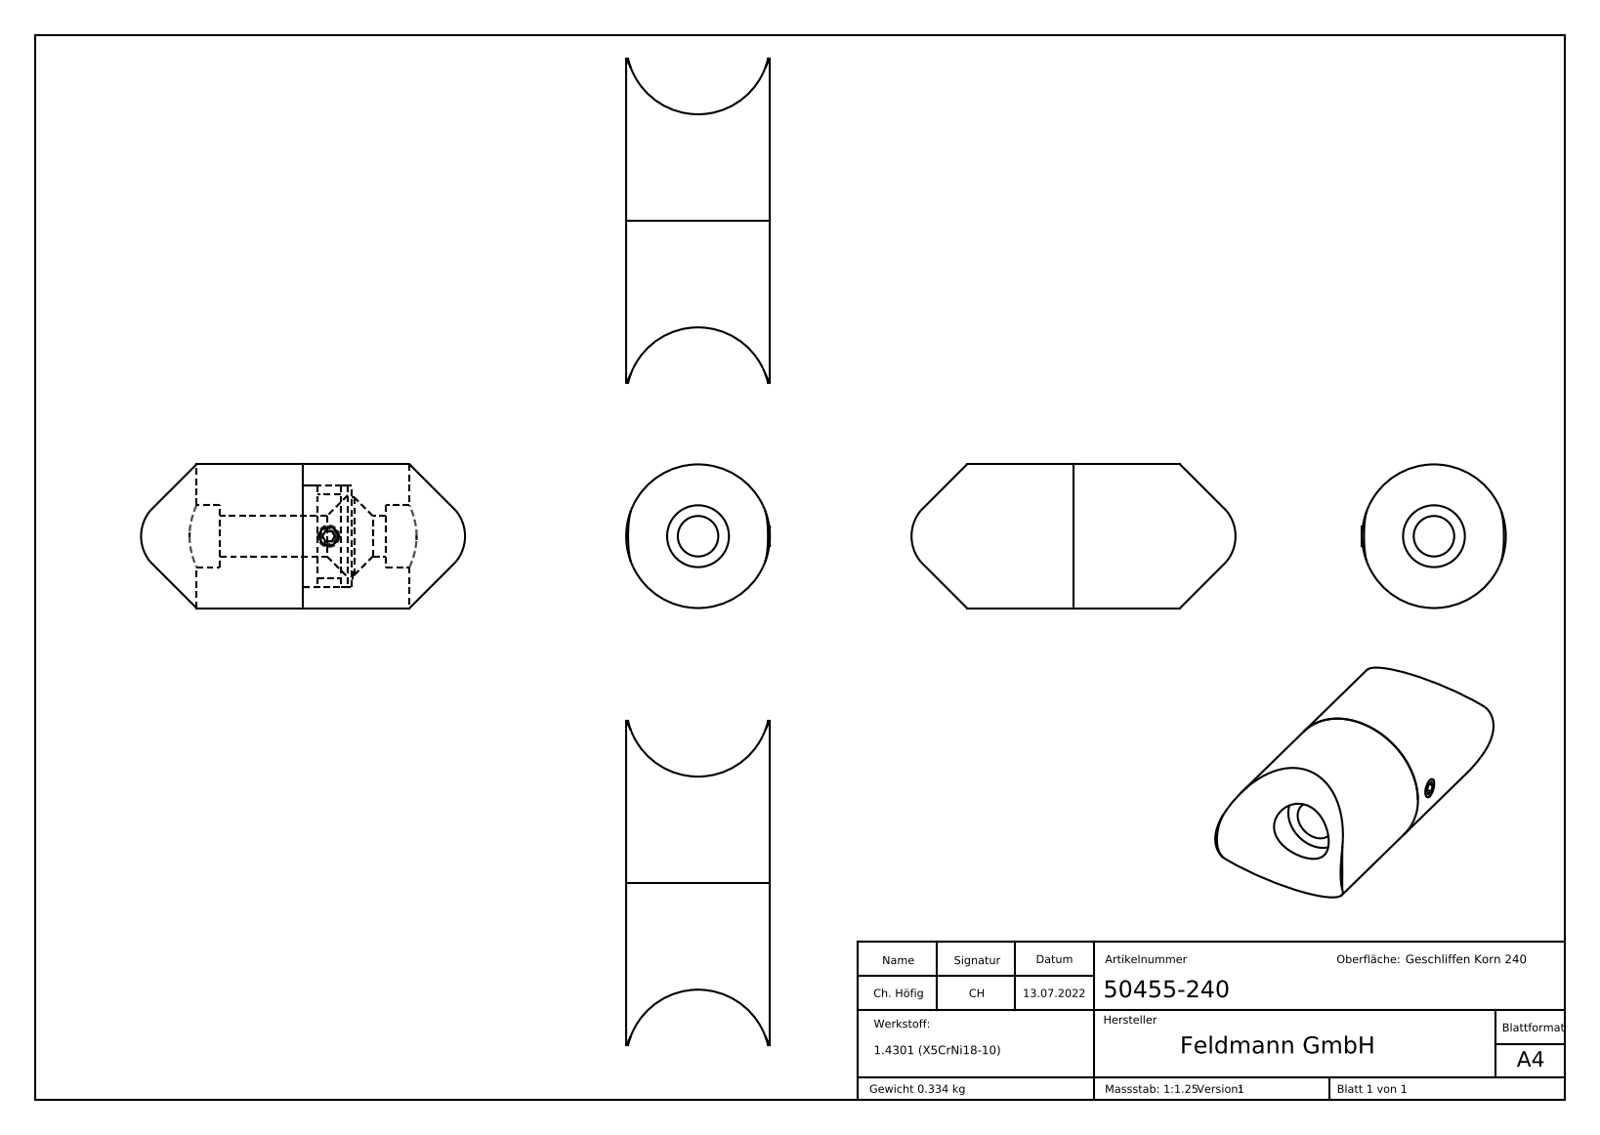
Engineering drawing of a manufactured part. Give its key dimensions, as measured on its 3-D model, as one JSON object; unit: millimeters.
{"part_name": "50455-240 DIN913 M5x6_DIN913 M5x6; 50455-240; 50455-240 Teil1_50455-240 Teil1; 50455-240 Teil2_50455-240 Teil2", "step_written_by": "SolidWorks 2018 (CONFIG_CONTROL_DESIGN)", "units": "millimeters", "bodies": {"solids": 3, "faces": 268, "planar": 149, "cylindrical": 19, "other": 100}, "overall_size": [76, 33.7, 33.7], "volume_mm3": 42275, "surface_area_mm2": 13877, "round_holes": [[4.2, 1], [9.5, 1], [14.5, 1], [18.25, 1], [24, 1]], "round_bosses_or_shafts": [[33.7, 1], [23.75, 1], [19.75, 1], [5, 1]], "partial_cylinders_radius": [[9.43, 2], [16.85, 2]], "face_to_face_distances": [11.5, 19.5, 1, 10.5, 2.7, 1.7, 8.8, 8.2, 7.2, 5.5]}
